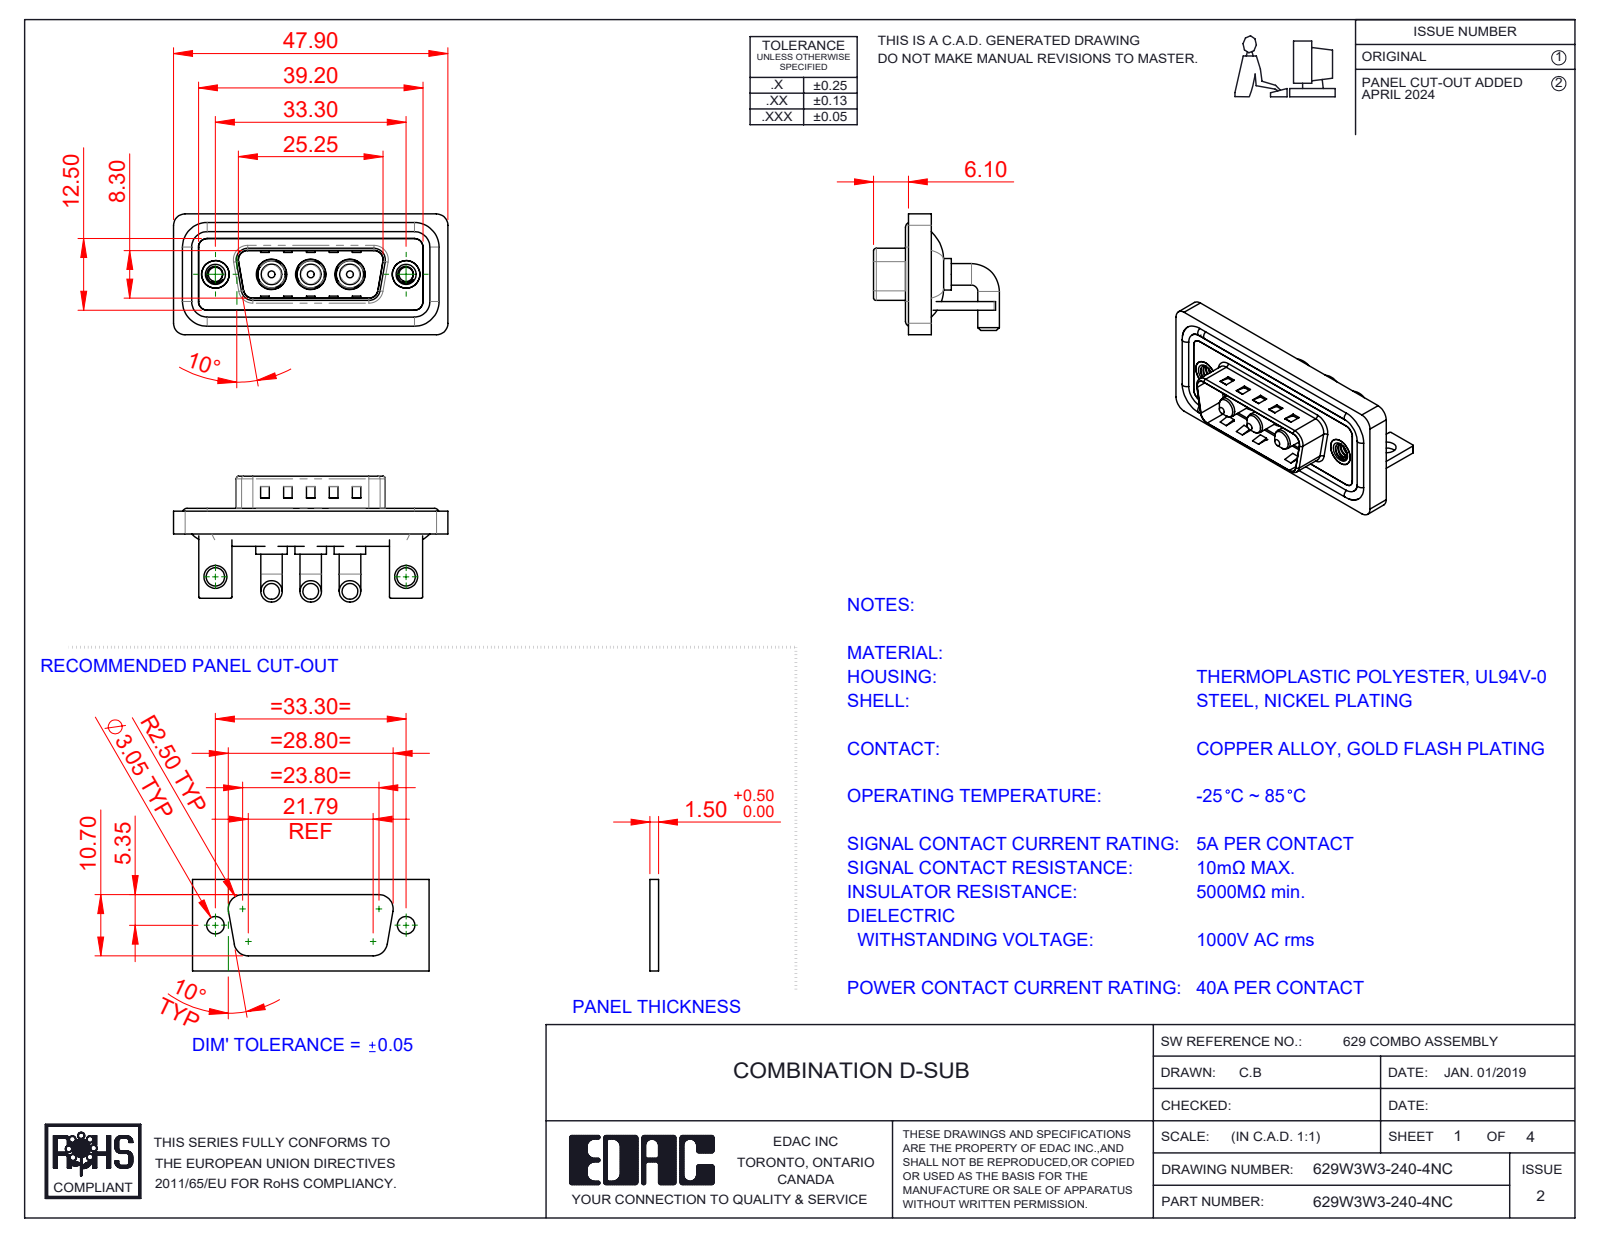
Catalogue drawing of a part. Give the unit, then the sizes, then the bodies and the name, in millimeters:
Units: millimetres
Overall size (bounding box): 47.9 × 21.98 × 21.1
Round holes (diameter × count): ⌀4.85 ×3, ⌀5.3 ×3, ⌀2.5 ×2, ⌀3.2 ×2, ⌀4 ×2, ⌀4.8 ×2, ⌀5 ×2
Round bosses / shafts (diameter × count): ⌀3.75 ×6, ⌀1.6 ×4, ⌀5.5 ×3, ⌀5.2 ×3, ⌀4.75 ×3, ⌀3.6 ×3, ⌀4.9 ×2
Partial cylindrical surfaces — rounded edges, fillets, slot ends (radius × count): R2 ×21, R1.5 ×18, R0.25 ×16, R0.5 ×9, R1.6 ×8, R0.6 ×4, R0.65 ×4, R0.9 ×4
Main face-to-face distances: 0.4, 1.5, 0.8, 2.9, 1.1, 2.1, 3.7, 1.6, 1.2, 4.5
Hole centre spacings: 6.85, 9.8, 16.65, 23.5, 33.3, 13.7
Volume: 6 269 mm³ · Surface area: 9 756 mm²
Bodies: 15 solids, 614 faces (227 planar, 265 cylindrical, 122 other)
Part name (STEP PRODUCT): 629W3W3-140-4NC; 629Combo Shell Rear_15 Contacts; 629Combo Housing_3W3; 629Combo Stabilizer Bracket (+4 more)
STEP written by: SolidWorks 2023 (CONFIG_CONTROL_DESIGN)
